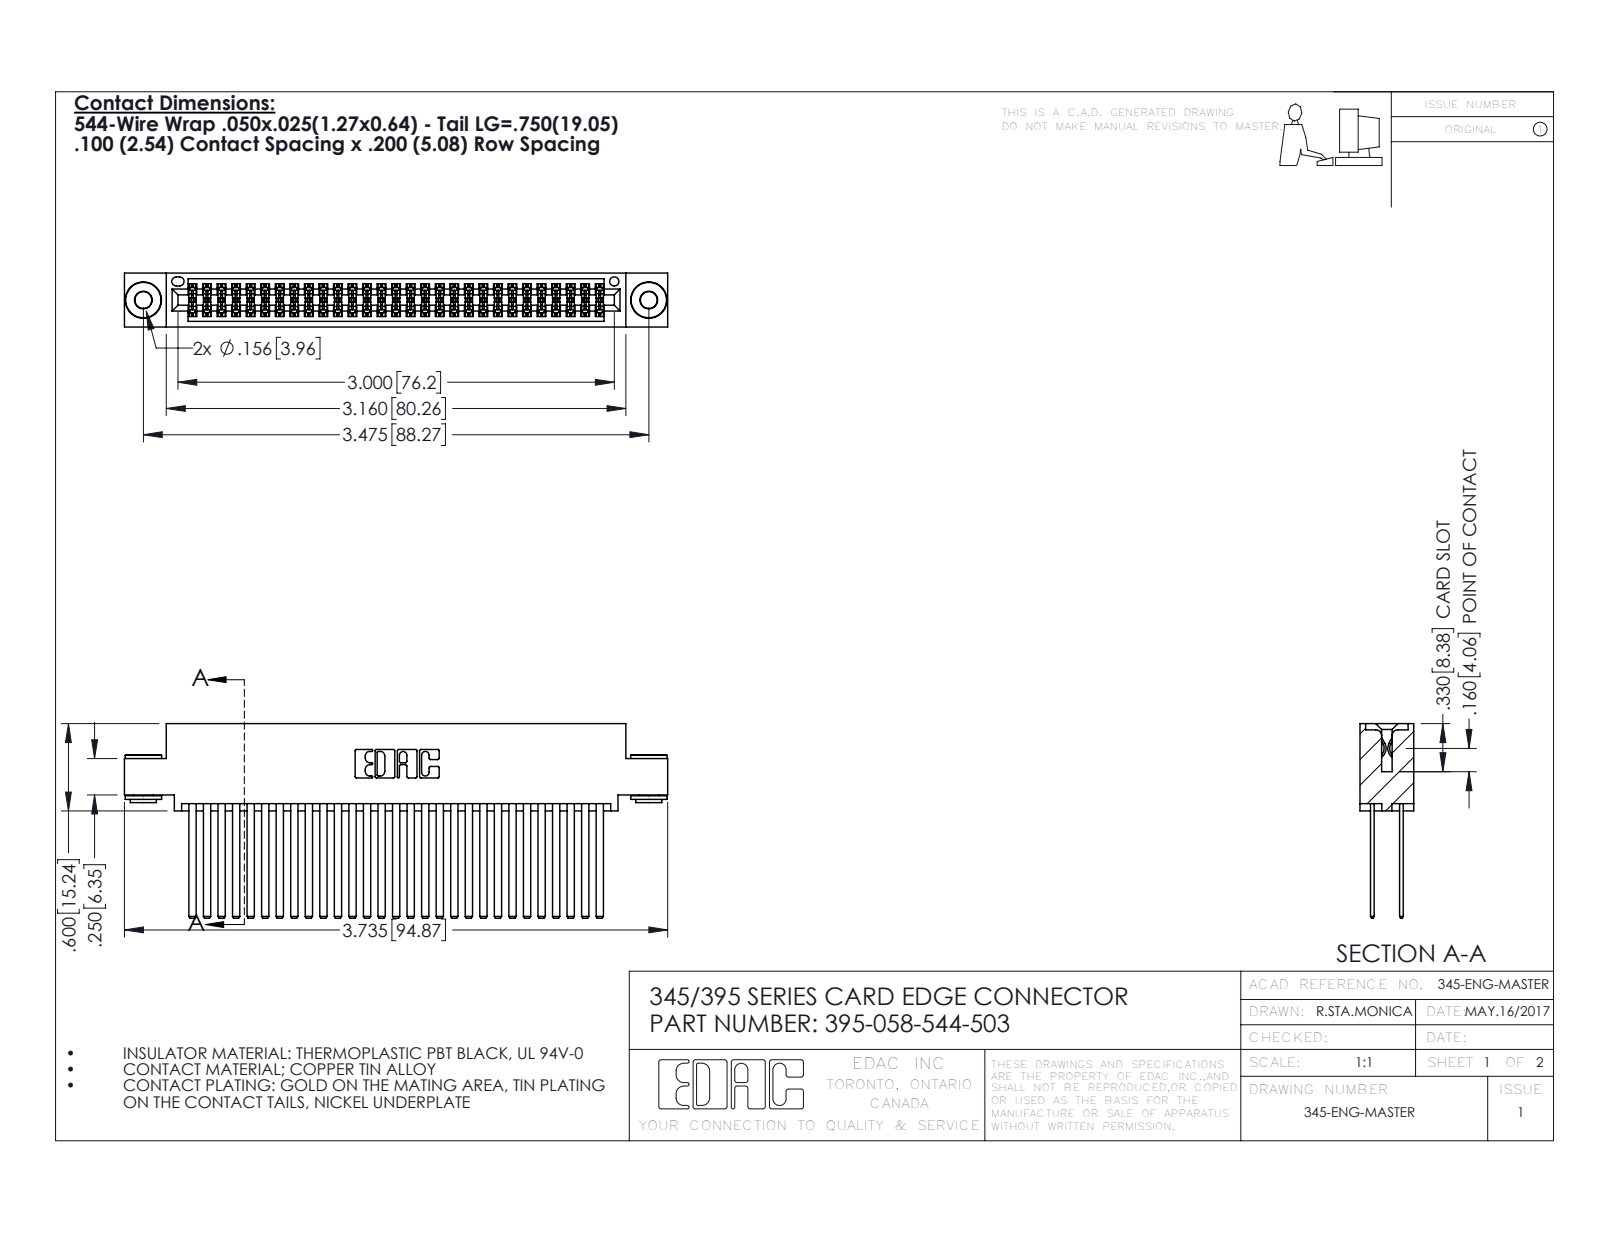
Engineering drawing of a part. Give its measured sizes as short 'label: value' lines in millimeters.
name: 345-292-001_345-293-144; 345-250-002_345-250-002-102; 345 Part_0.110 Offset - 0.156 Dia-TH; 395-058-544-503
written by: SolidWorks 2016 (CONFIG_CONTROL_DESIGN)
unit: mm
bodies: 61 solids, 2720 faces (1776 planar, 936 cylindrical, 8 other)
size: 94.9 × 34 × 9.4
volume: 9 850 mm³; area: 16 990 mm²
holes: 2× ⌀2.9, 2× ⌀4, 1× ⌀1.6
bosses: 2× ⌀6.4, 2× ⌀4.6, 2× ⌀3.5
rounds: 87× R0.2, 22× R0.3, 6× R0.2, 6× R0.8, 3× R0.7, 2× R0.4, 2× R0.5, 2× R0.6
face distances: 5.1, 0.6, 1.8, 7.6, 2.5, 6.9, 5.7, 4.4, 9.4, 1.3
hole spacings: 6.9, 82.3, 88.3
